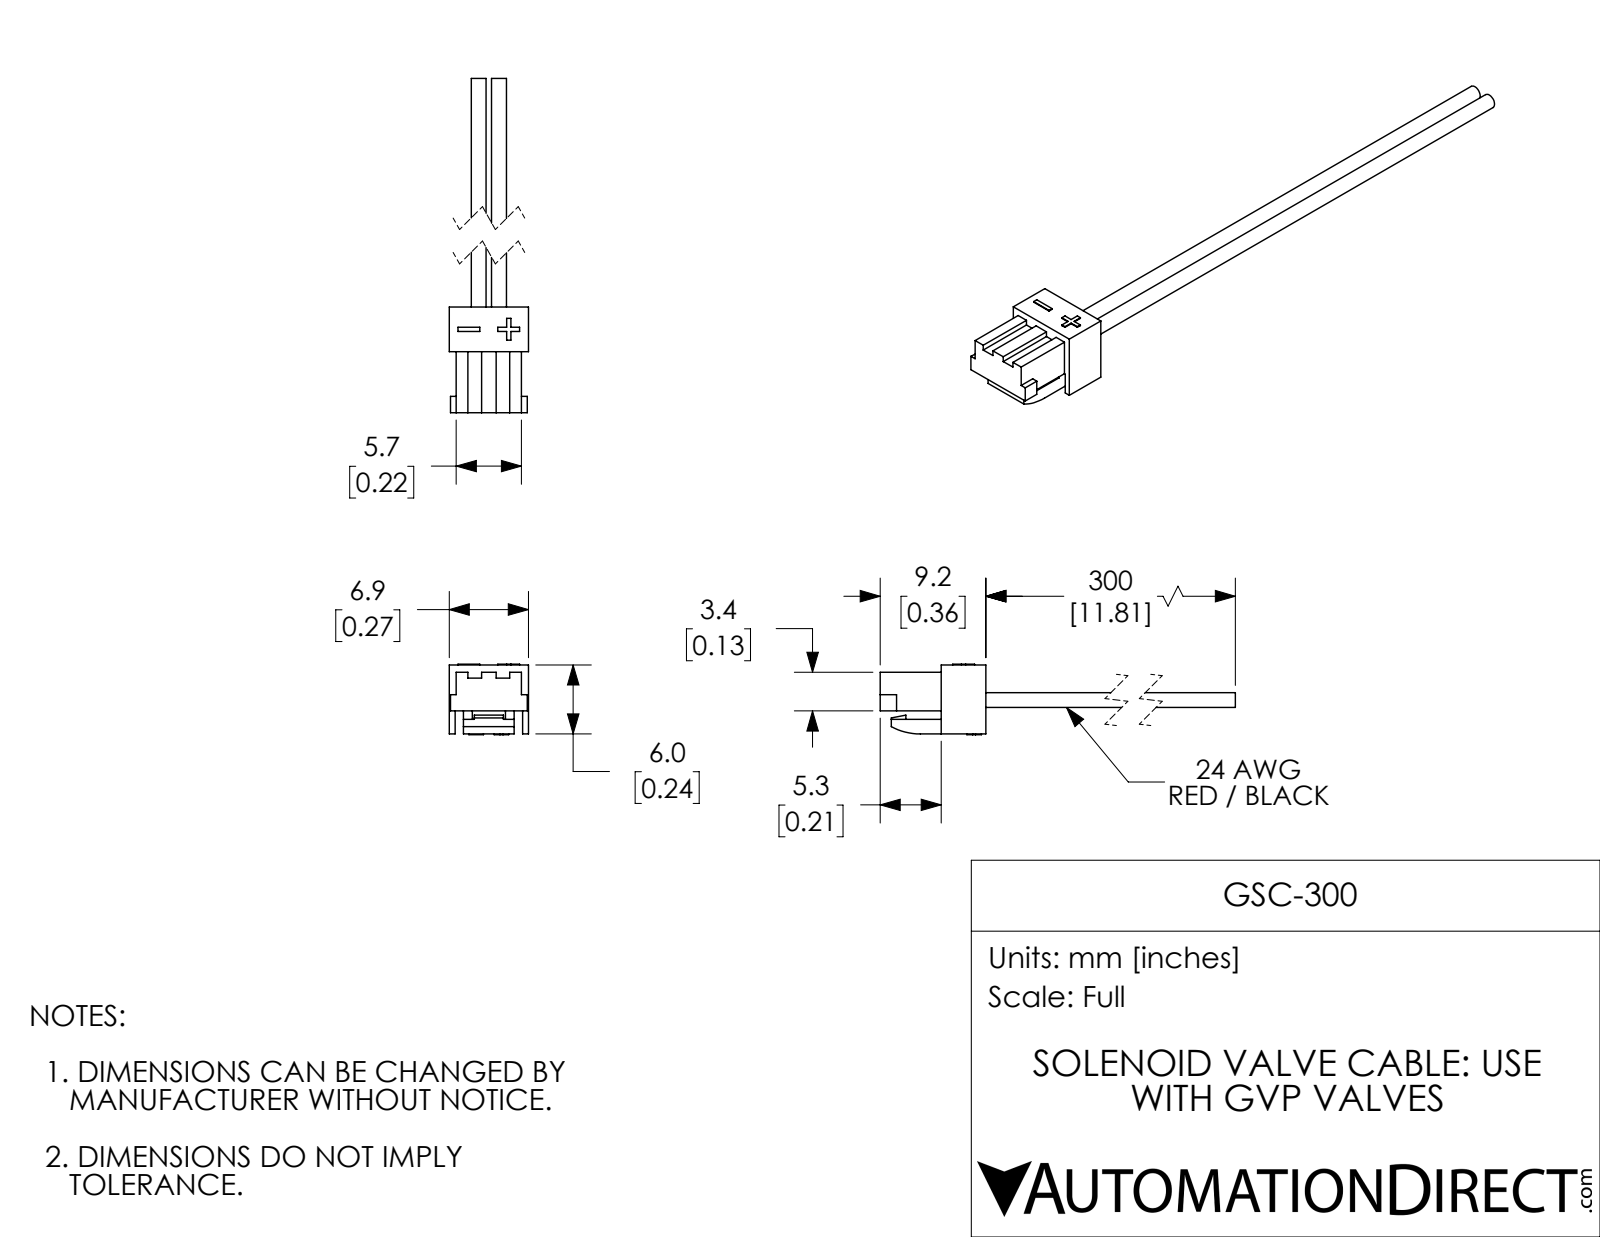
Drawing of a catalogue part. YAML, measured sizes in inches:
part_name: "GSC-300"
step_written_by: "SolidWorks 2018 (AUTOMOTIVE_DESIGN)"
units: inches
bodies: {solids: 1, faces: 97, planar: 92, cylindrical: 5, other: 0}
overall_size: [2.353, 0.272, 0.242]
volume: 0.024
surface_area: 1.259
round_bosses_or_shafts:
  - {diameter: 0.051, count: 2}
partial_cylinders:
  - {radius: 0.213, count: 1}
face_to_face_distances: [0.029, 0.024, 0.05, 0.248, 0.02, 0.079, 0.237, 0.187, 0.158, 0.272]
